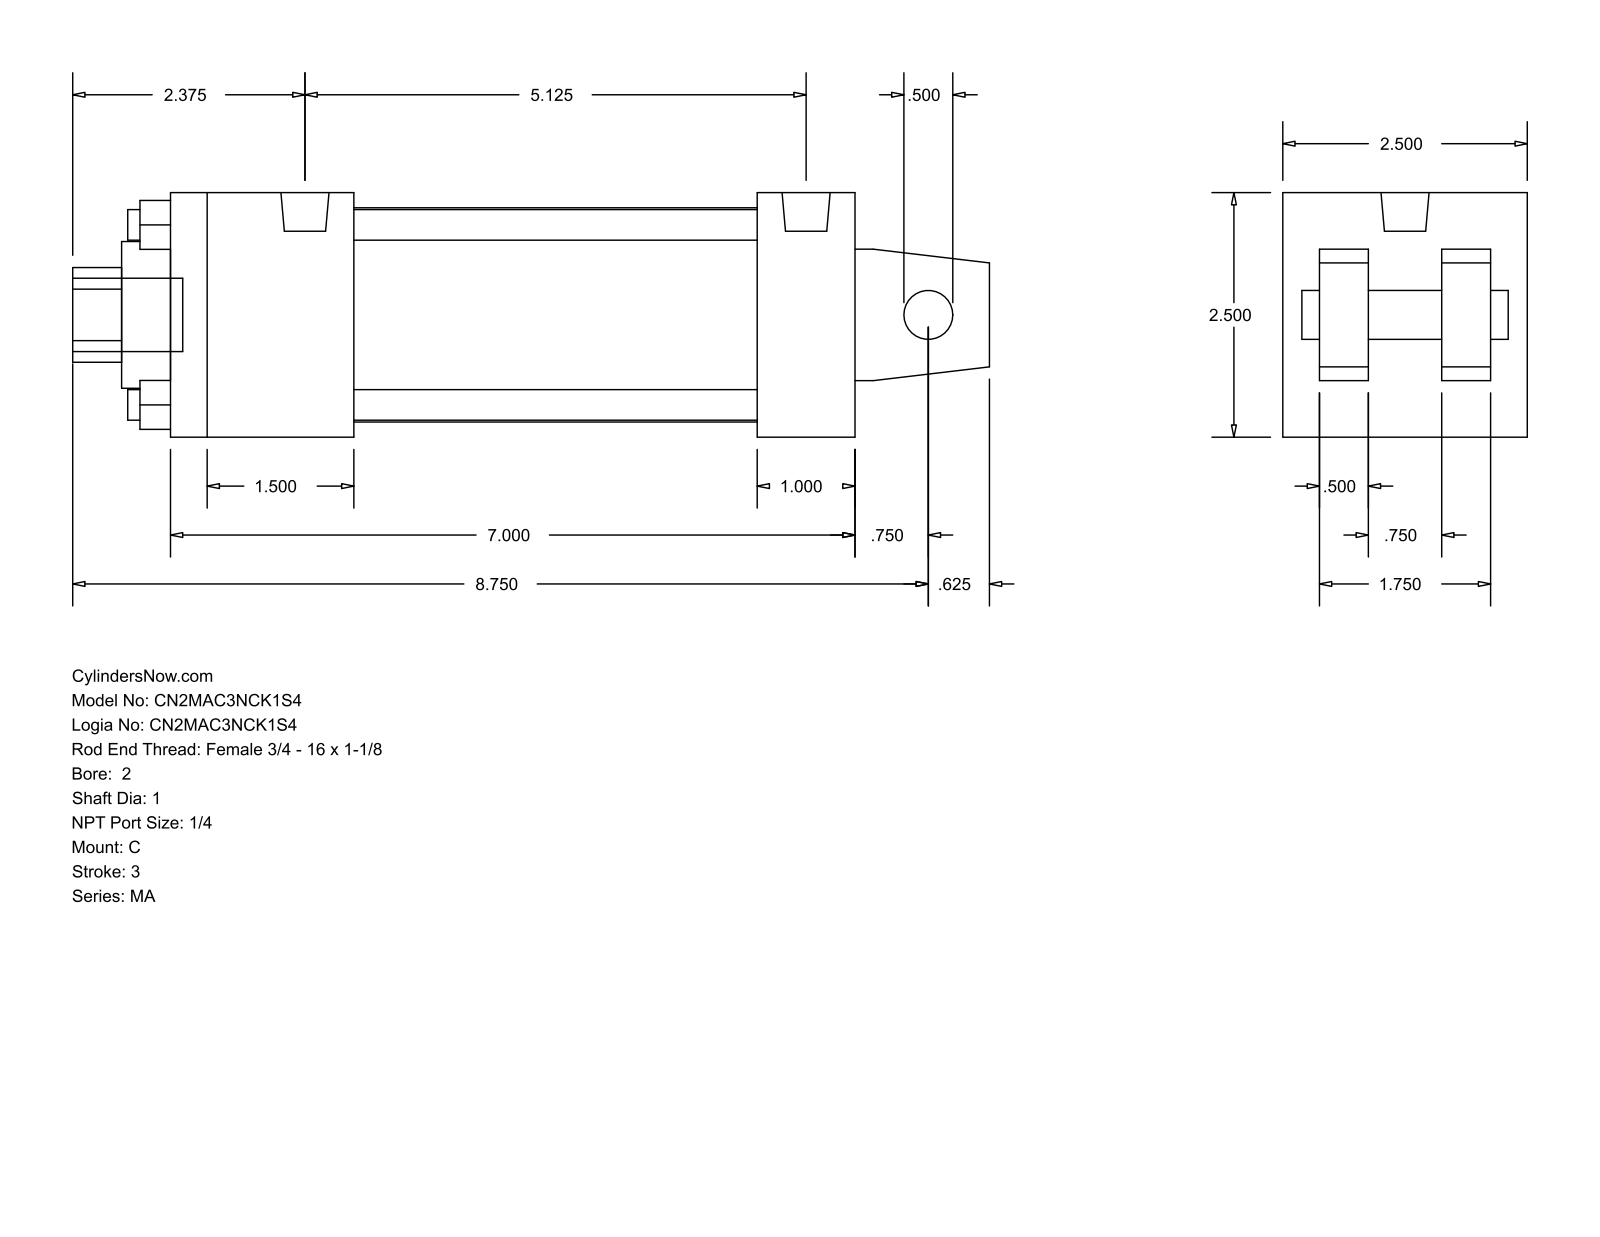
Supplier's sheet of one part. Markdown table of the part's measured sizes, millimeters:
| quantity | value |
| --- | --- |
| part name | MA_C__0200_1 |
| STEP written by | GSSL Pune (CONFIG_CONTROL_DESIGN) |
| units | millimeters |
| bodies | 0 solids, 103 faces (76 planar, 27 cylindrical, 0 other) |
| overall size | 238.12 × 63.5 × 63.5 |
| round holes (diameter × count) | 7.94 × 4, 12.7 × 1, 25.4 × 1, 38.1 × 1, 55.63 × 1 |
| round bosses / shafts (diameter × count) | 7.94 × 4, 12.49 × 2, 19.05 × 1 |
| partial cylindrical surfaces (radius × count) | 12.29 × 1 |
| main face-to-face distances | 63.5, 12.7, 177.8, 22.22, 41.28, 9.52, 53.98, 31.76, 47.63, 25.4 |
| hole center spacings | 33.05, 46.74, 66.1 |
